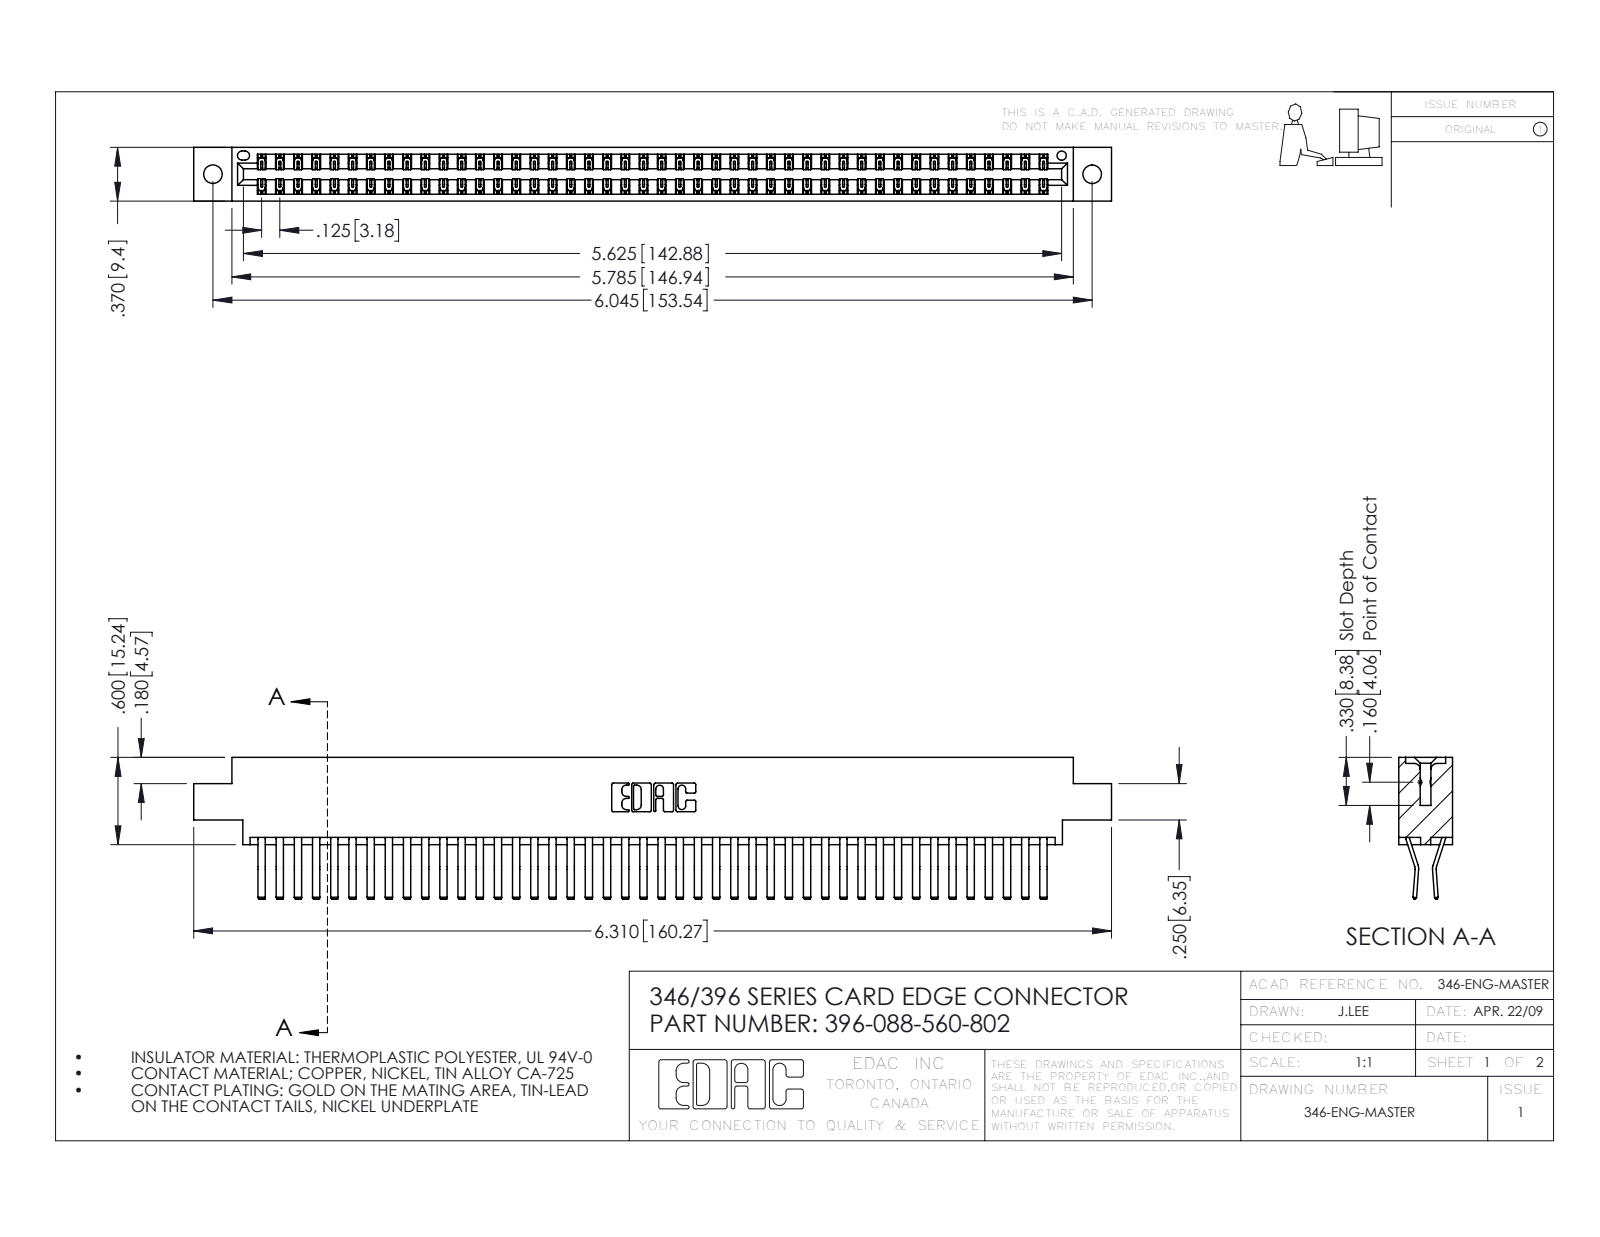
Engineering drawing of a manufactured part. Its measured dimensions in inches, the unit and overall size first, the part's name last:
Units: inches
Overall size (bounding box): 6.31 × 0.975 × 0.37
Round holes (diameter × count): ⌀0.128 ×2, ⌀0.064 ×1
Partial cylindrical surfaces — rounded edges, fillets, slot ends (radius × count): R0.006 ×132, R0.01 ×22, R0.007 ×6, R0.031 ×6, R0.026 ×3, R0.01 ×2, R0.014 ×2, R0.022 ×2
Main face-to-face distances: 0.048, 0.322, 0.37, 0.025, 0.25, 0.072, 0.298, 0.275, 0.148, 0.222
Hole centre spacings: 0.246, 5.836, 6.045
Volume: 0.978 in³ · Surface area: 36.45 in²
Bodies: 89 solids, 4878 faces (3160 planar, 1718 cylindrical, 0 other)
Part name (STEP PRODUCT): 345-292-001_560 Tail; 346 Part_0.170 Offset - 0.128 Dia; 396-088-560-802
STEP written by: SolidWorks 2016 (CONFIG_CONTROL_DESIGN)
